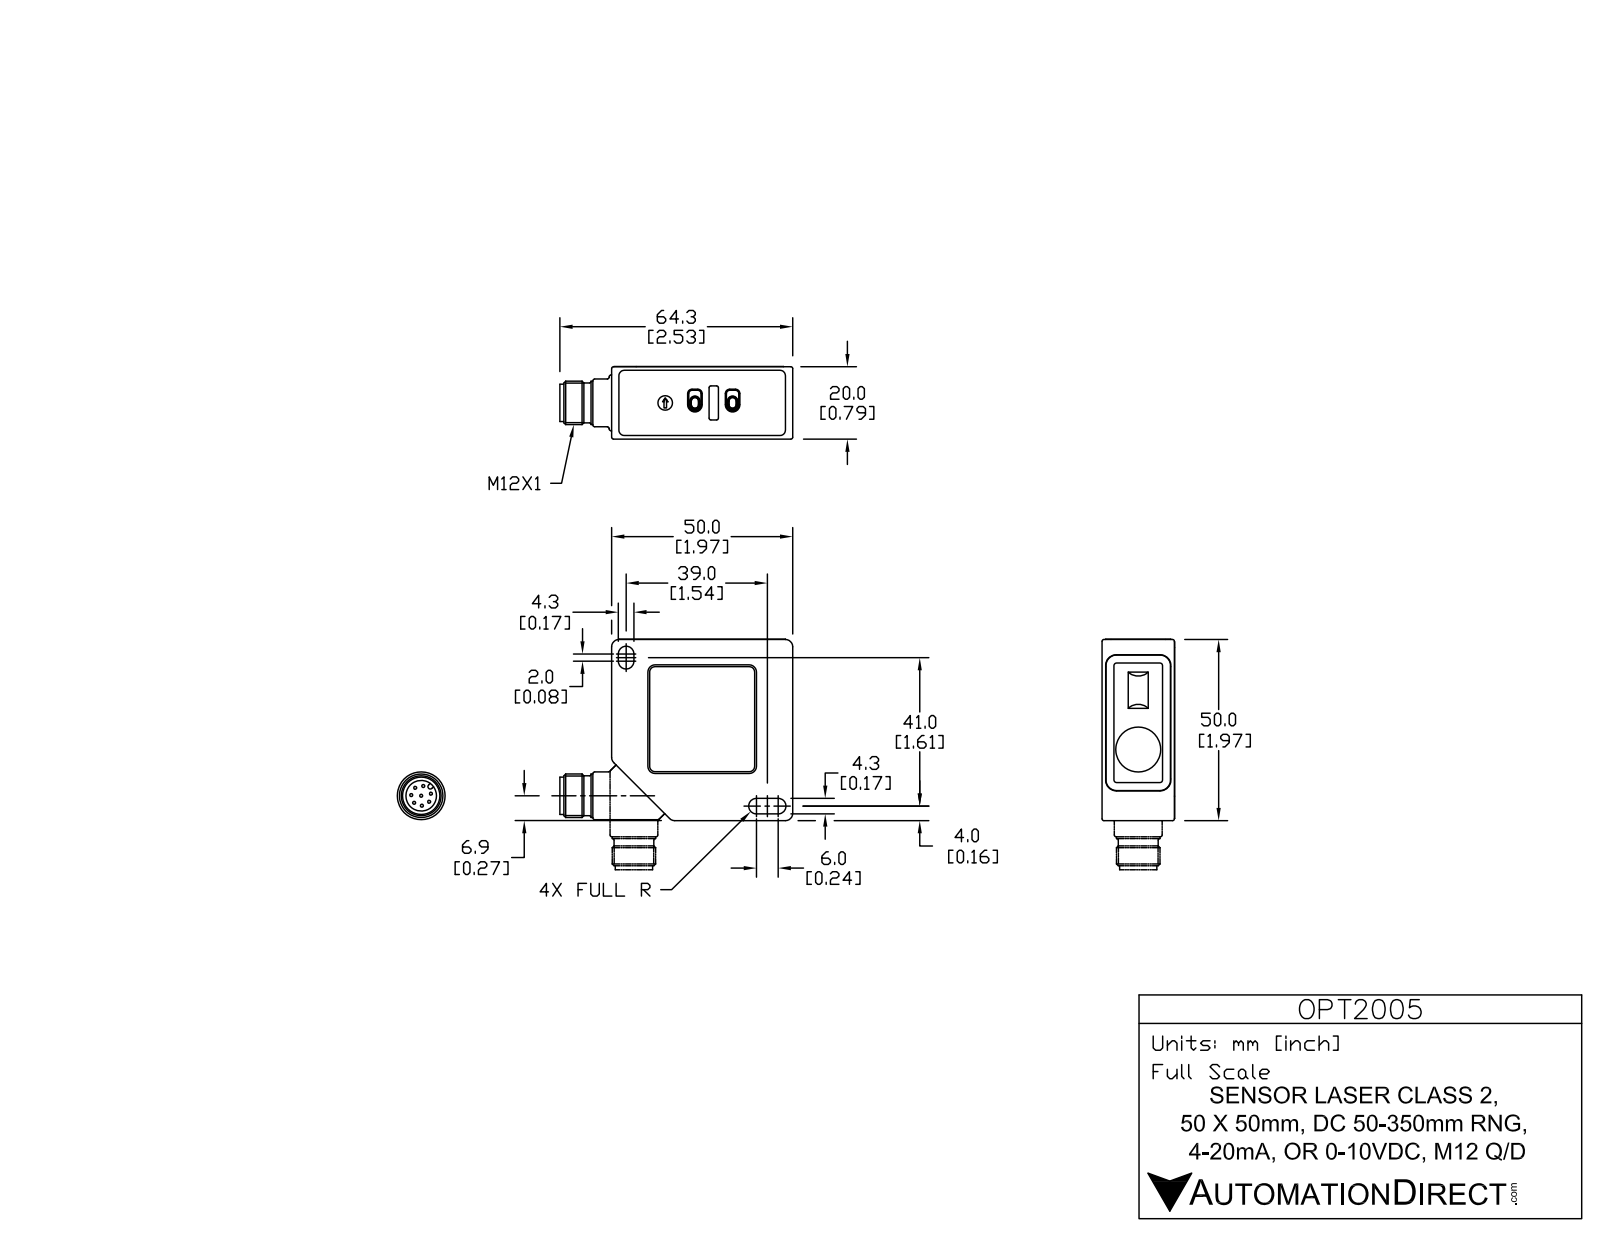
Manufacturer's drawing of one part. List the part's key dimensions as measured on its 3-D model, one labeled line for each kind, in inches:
Part name (STEP PRODUCT): OPT2005
STEP written by: SolidWorks 2013 (AUTOMOTIVE_DESIGN)
Units: inches
Bodies: 15 solids, 301 faces (153 planar, 134 cylindrical, 14 other)
Overall size (bounding box): 2.537 × 1.972 × 0.787
Volume: 2.969 in³ · Surface area: 24.84 in²
Round holes (diameter × count): ⌀0.157 ×1, ⌀0.333 ×1
Round bosses / shafts (diameter × count): ⌀0.032 ×8, ⌀0.709 ×1, ⌀0.531 ×1, ⌀0.488 ×1, ⌀0.472 ×1, ⌀0.433 ×1, ⌀0.406 ×1
Partial cylindrical surfaces — rounded edges, fillets, slot ends (radius × count): R0.079 ×17, R0.008 ×10, R0.039 ×8, R0.083 ×5, R0.02 ×4, R0.047 ×4, R0.085 ×4, R0.114 ×4
Main face-to-face distances: 0.787, 0.78, 1.969, 1.972, 1.902, 0.063, 1.906, 0.21, 2.111, 2.115
